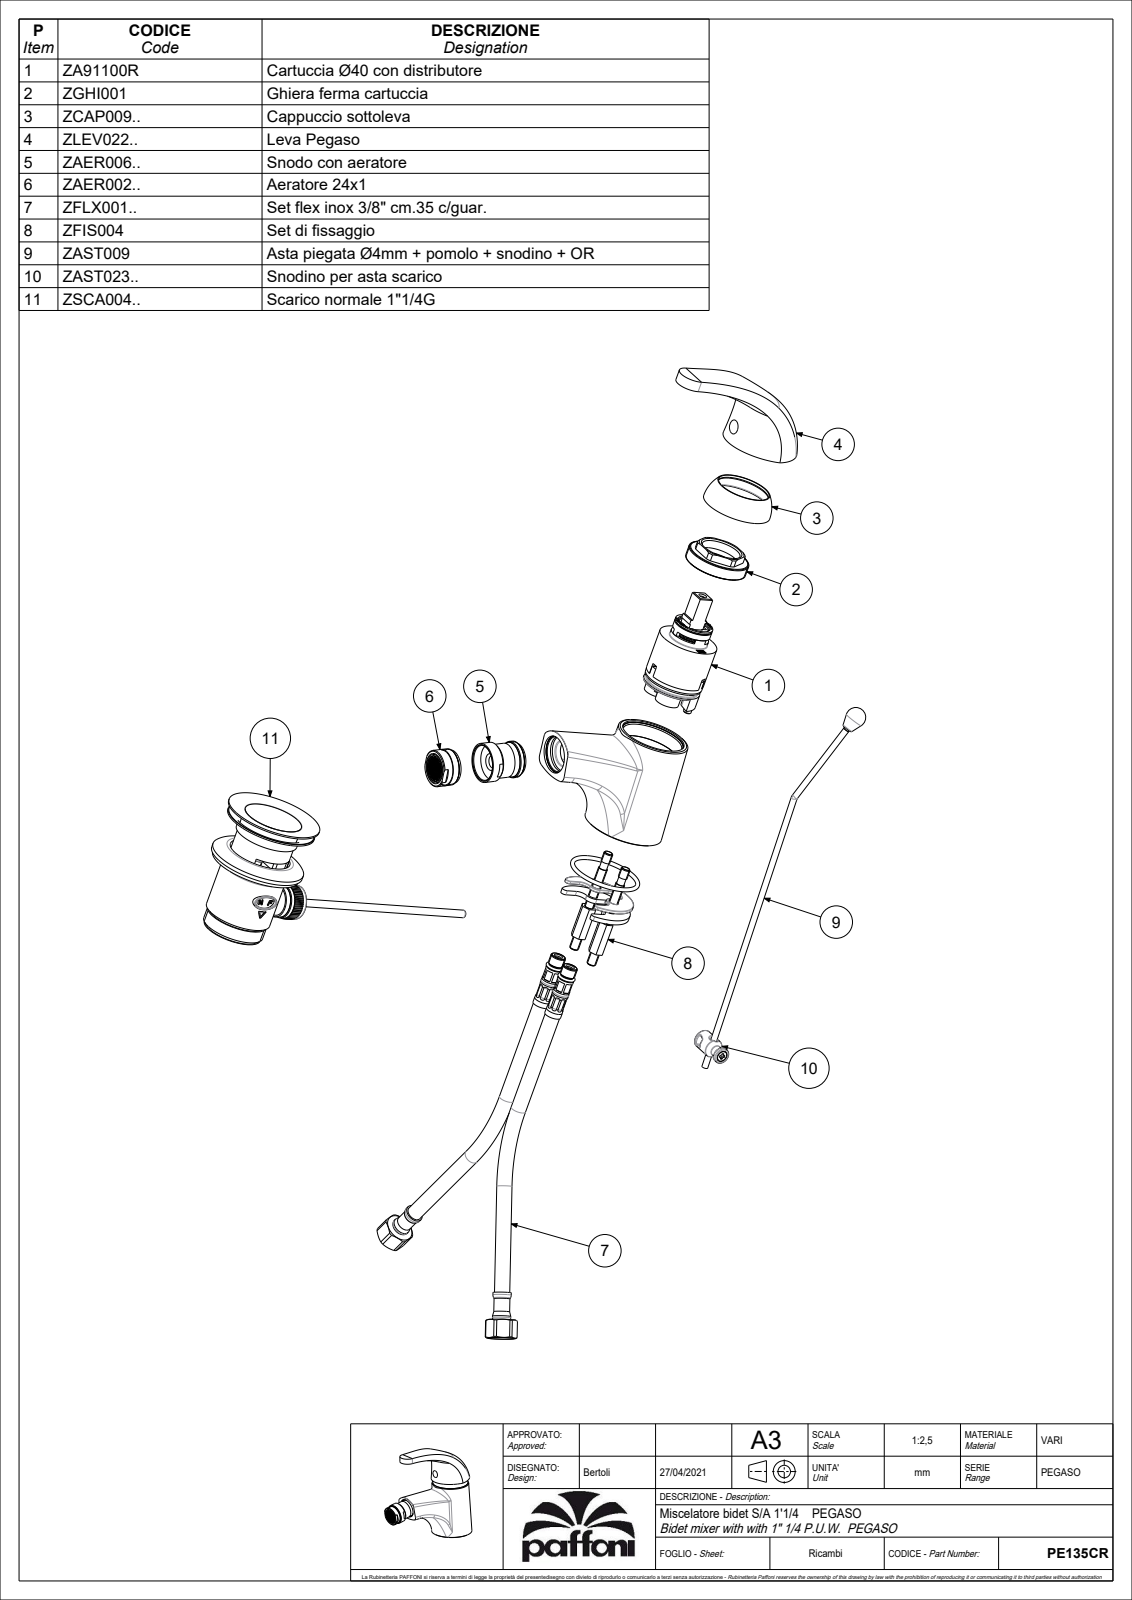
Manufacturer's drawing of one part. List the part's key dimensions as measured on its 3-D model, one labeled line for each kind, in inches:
Part name (STEP PRODUCT): PE135CR_SW0001
STEP written by: CREO PARAMETRIC BY PTC INC, 2022124 (CONFIG_CONTROL_DESIGN)
Units: inches
Bodies: 3 solids, 588 faces (157 planar, 208 cylindrical, 223 other)
Overall size (bounding box): 5.764 × 4.806 × 2.082
Volume: 8.386 in³ · Surface area: 111.5 in²
Round holes (diameter × count): ⌀0.315 ×4, ⌀0.433 ×3, ⌀0.207 ×2, ⌀0.276 ×2, ⌀0.354 ×2, ⌀0.472 ×2, ⌀0.157 ×1, ⌀0.217 ×1, ⌀0.236 ×1, ⌀0.295 ×1, ⌀0.591 ×1, ⌀0.61 ×1
Round bosses / shafts (diameter × count): ⌀0.394 ×3, ⌀0.626 ×2, ⌀0.37 ×2, ⌀1.642 ×1, ⌀1.543 ×1, ⌀1.528 ×1, ⌀1.37 ×1, ⌀1.016 ×1
Partial cylindrical surfaces — rounded edges, fillets, slot ends (radius × count): R0.02 ×44, R0.039 ×8, R0.079 ×5, R0.012 ×4, R0.059 ×4, R0.197 ×3, R0.354 ×3, R0.217 ×2
Main face-to-face distances: 0.146, 0.512, 0.059, 0.079, 0.354, 0.591, 0.138, 0.157, 0.689, 0.177
Hole centre spacings: 0.028, 0.062, 0.079, 0.339, 0.366, 0.39, 0.404, 0.432
